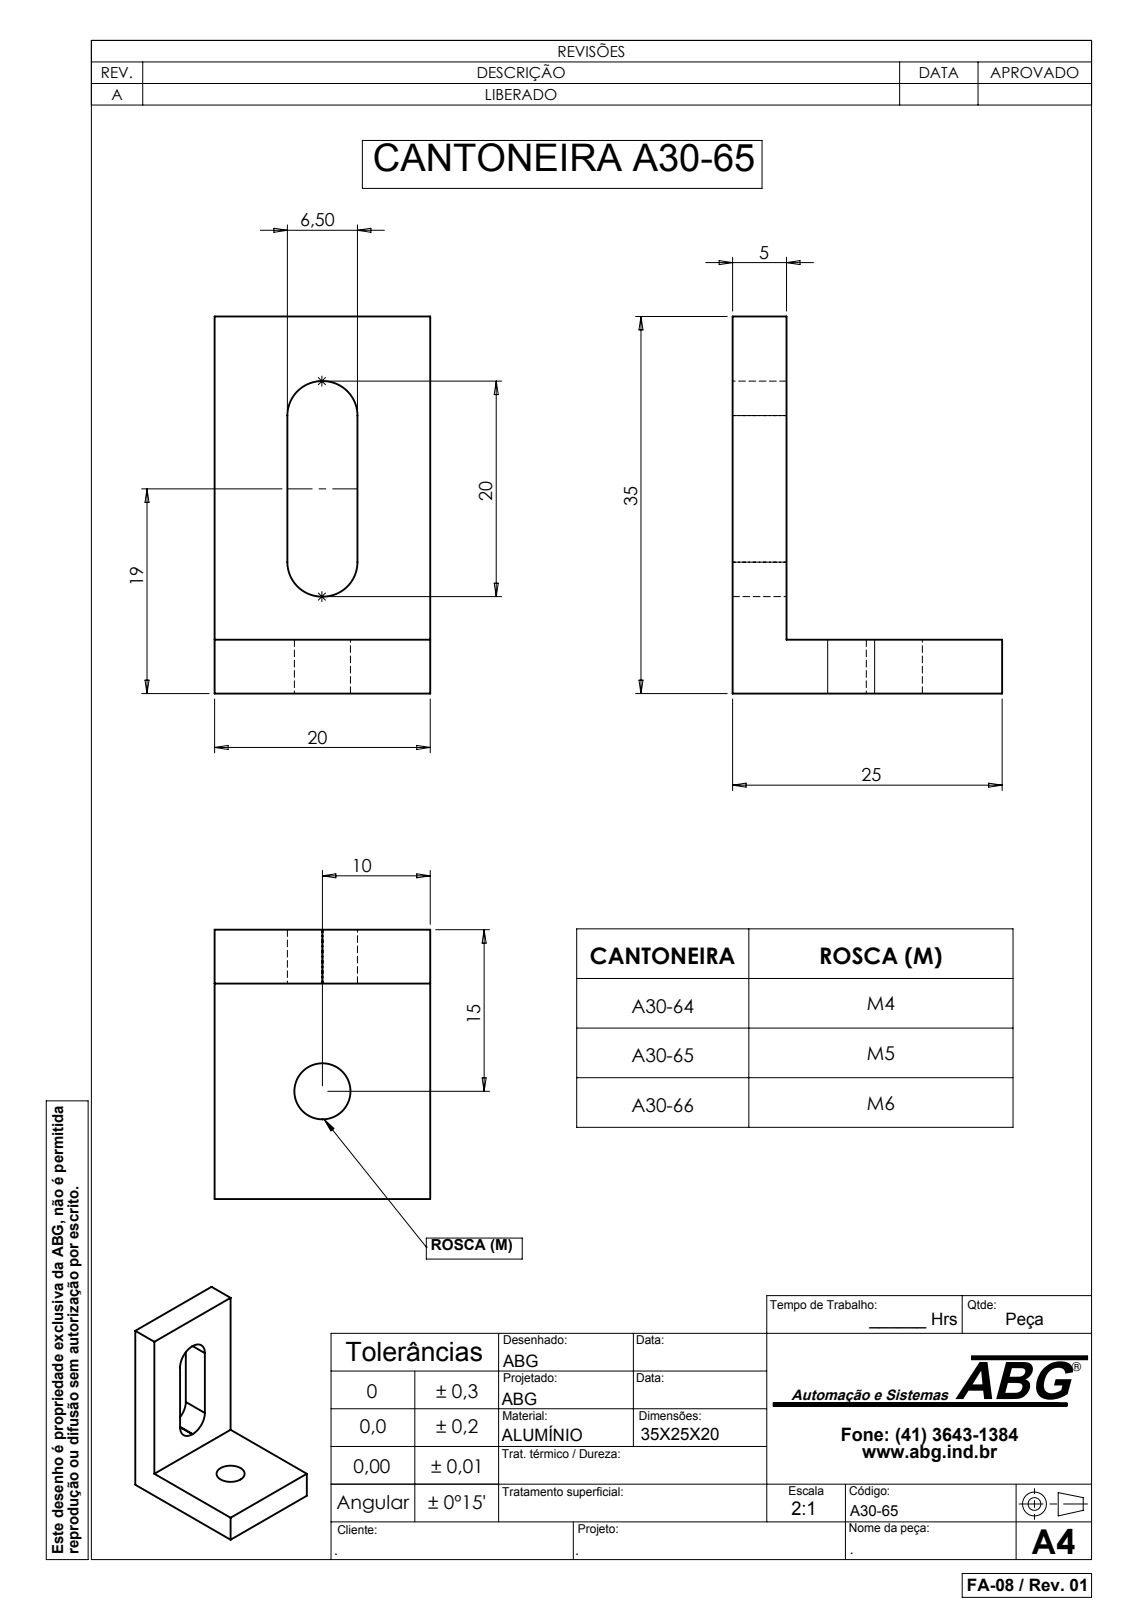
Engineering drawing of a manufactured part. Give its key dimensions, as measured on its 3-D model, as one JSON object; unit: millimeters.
{"part_name": "A30-65", "step_written_by": "SolidWorks 2007 (CONFIG_CONTROL_DESIGN)", "units": "millimeters", "bodies": {"solids": 1, "faces": 18, "planar": 12, "cylindrical": 6, "other": 0}, "overall_size": [35, 25, 20], "volume_mm3": 4796, "surface_area_mm2": 2984, "round_holes": [[5, 1]], "partial_cylinders_radius": [[3.2, 4]], "face_to_face_distances": [5, 20, 6.75, 13.25, 30, 35, 25, 6.5, 6, 24]}
